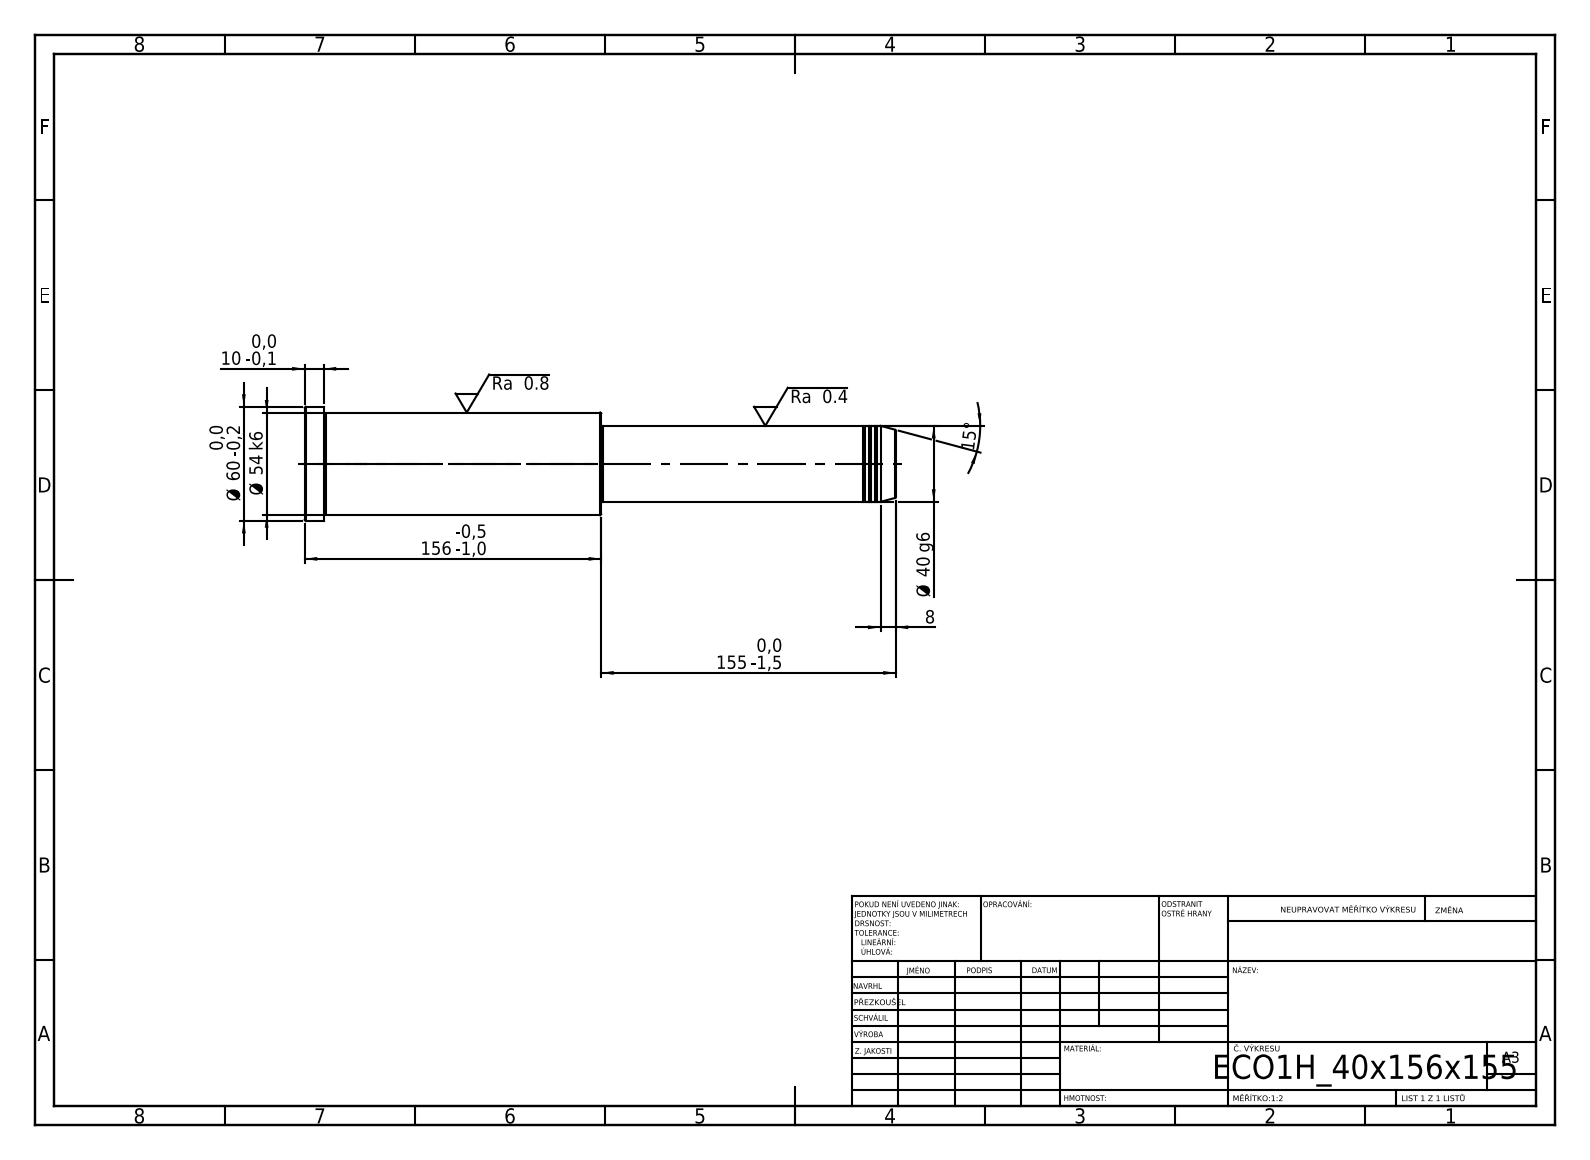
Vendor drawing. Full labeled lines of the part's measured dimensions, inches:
STEP written by: SolidWorks 2019 (CONFIG_CONTROL_DESIGN)
Units: inches
Bodies: 1 solid, 43 faces (5 planar, 14 cylindrical, 24 other)
Overall size (bounding box): 12.244 × 2.362 × 2.362
Volume: 33.93 in³ · Surface area: 80.31 in²
Round bosses / shafts (diameter × count): ⌀2.362 ×1, ⌀2.126 ×1, ⌀1.575 ×1, ⌀1.535 ×1
Main face-to-face distances: 6.142, 6.102, 12.244, 11.85, 5.748, 0.394, 6.063, 0.039, 5.787, 6.181
